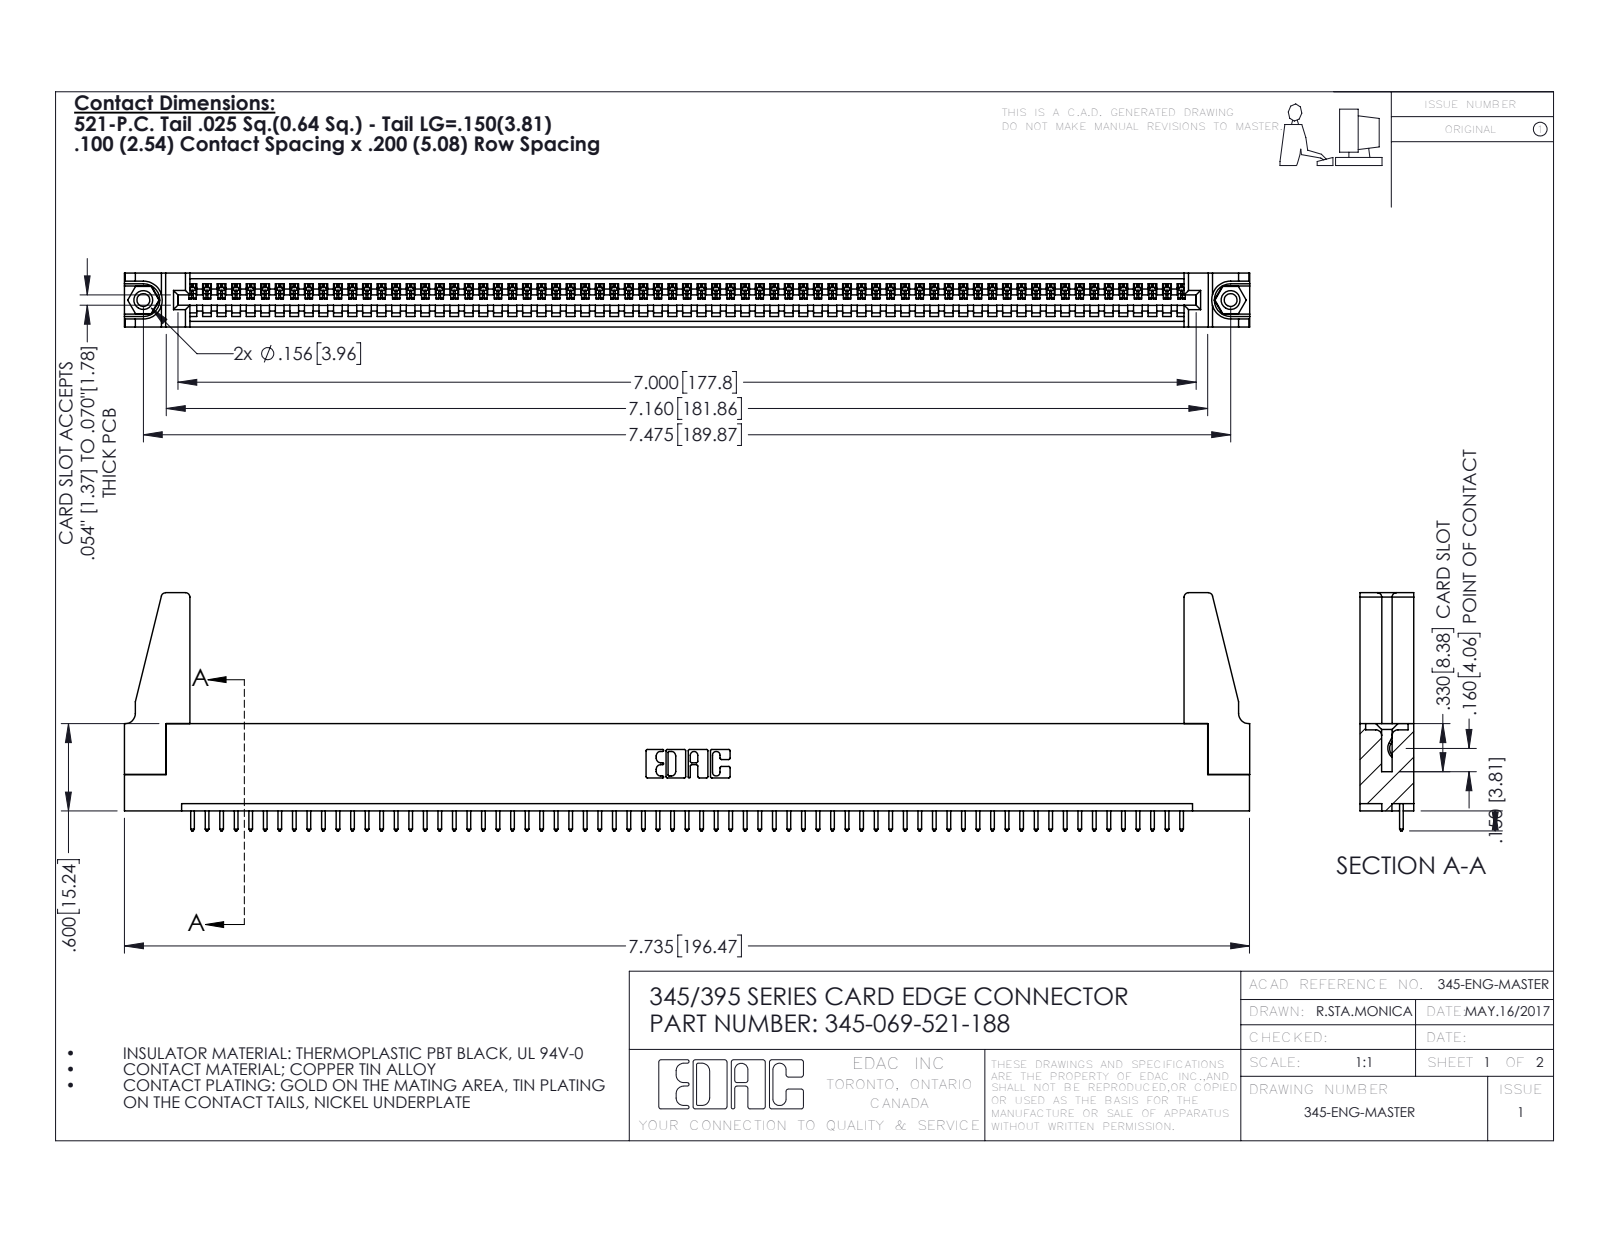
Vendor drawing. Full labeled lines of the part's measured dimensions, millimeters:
Part name (STEP PRODUCT): 345 Part_Flush Mounting Lugs - 0.156 Dia-TH; 345-069-521-188; 345-220-078_345-220-088; 345-292-001_345-293-121 (+1 more)
STEP written by: SolidWorks 2016 (CONFIG_CONTROL_DESIGN)
Units: millimetres
Bodies: 74 solids, 4252 faces (2912 planar, 1324 cylindrical, 16 other)
Overall size (bounding box): 196.5 × 41.6 × 9.4
Volume: 21 940 mm³ · Surface area: 27 560 mm²
Round holes (diameter × count): ⌀2.3 ×2, ⌀3.2 ×2, ⌀4 ×2, ⌀1.6 ×1
Round bosses / shafts (diameter × count): ⌀3.9 ×2
Partial cylindrical surfaces — rounded edges, fillets, slot ends (radius × count): R0.2 ×138, R0.3 ×138, R0.3 ×22, R0.8 ×8, R0.2 ×6, R0.8 ×6, R0.7 ×3, R0.8 ×2
Main face-to-face distances: 1.8, 7.6, 9.4, 5.1, 2.5, 6.9, 0.6, 5.7, 3.8, 1.8
Hole centre spacings: 6.9, 183.9, 189.9
